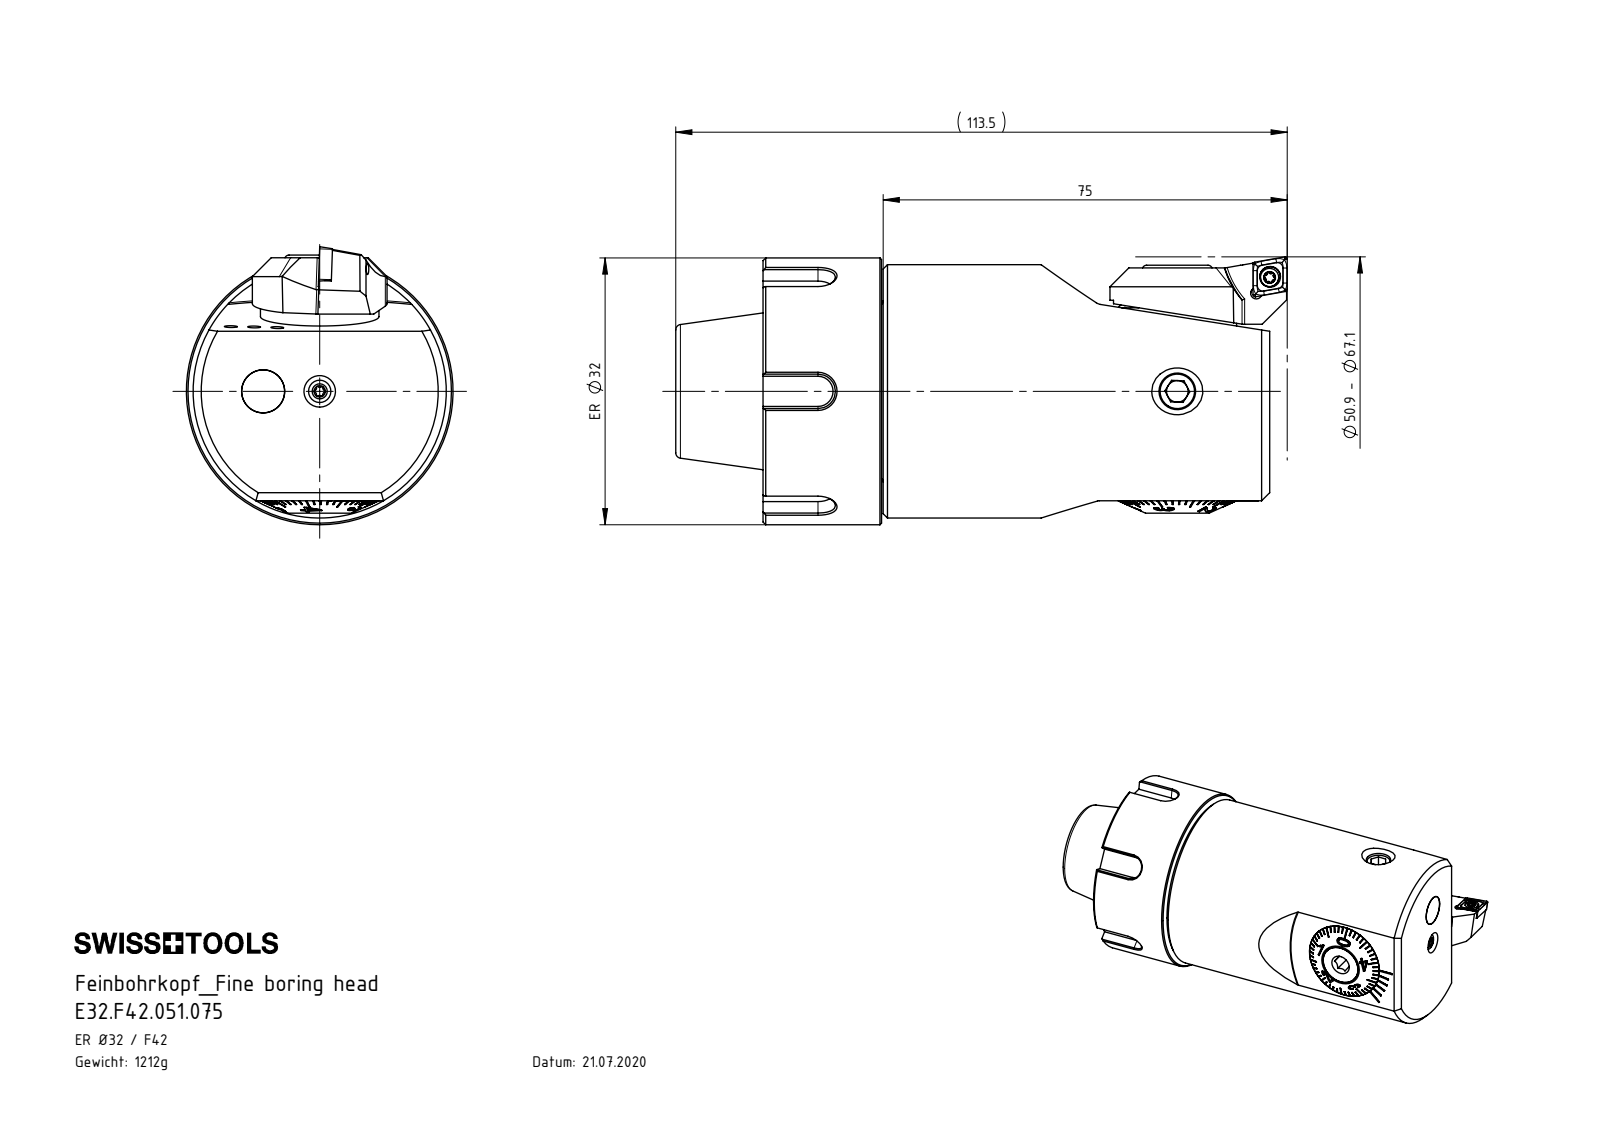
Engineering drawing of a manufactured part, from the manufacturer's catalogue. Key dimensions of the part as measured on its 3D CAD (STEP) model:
Part name (STEP PRODUCT): A42-BG1.012.006_B; PEF-DA3.010.032_A_F42; E32-F42.AA3.075_A_bohrungen gefllt; Klebstoff D8 (+8 more)
STEP written by: SolidWorks 2017 (AUTOMOTIVE_DESIGN)
Units: millimetres
Bodies: 32 solids, 778 faces (476 planar, 102 cylindrical, 200 other)
Overall size (bounding box): 110.25 × 49.5 × 49.5
Volume: 153 100 mm³ · Surface area: 42 387 mm²
Round holes (diameter × count): ⌀2.1 ×3, ⌀6.8 ×3, ⌀4.2 ×2, ⌀2.5 ×1, ⌀3 ×1, ⌀3.2 ×1, ⌀3.3 ×1, ⌀3.9 ×1, ⌀4 ×1, ⌀6 ×1, ⌀8 ×1, ⌀8.5 ×1
Round bosses / shafts (diameter × count): ⌀1.9 ×6, ⌀8 ×2, ⌀3.8 ×2, ⌀2 ×2, ⌀49.5 ×1, ⌀47 ×1, ⌀32 ×1, ⌀29.5 ×1
Partial cylindrical surfaces — rounded edges, fillets, slot ends (radius × count): R0.21 ×6, R1.1 ×6, R0.36 ×5, R1.4 ×4, R0.5 ×3, R3.2 ×3, R2 ×2, R0.36 ×1
Main face-to-face distances: 72.05, 71.75, 22, 22.3, 94.05, 5.6, 38.5, 38.2, 16.2, 2.7
Hole centre spacings: 10.5, 12.33
